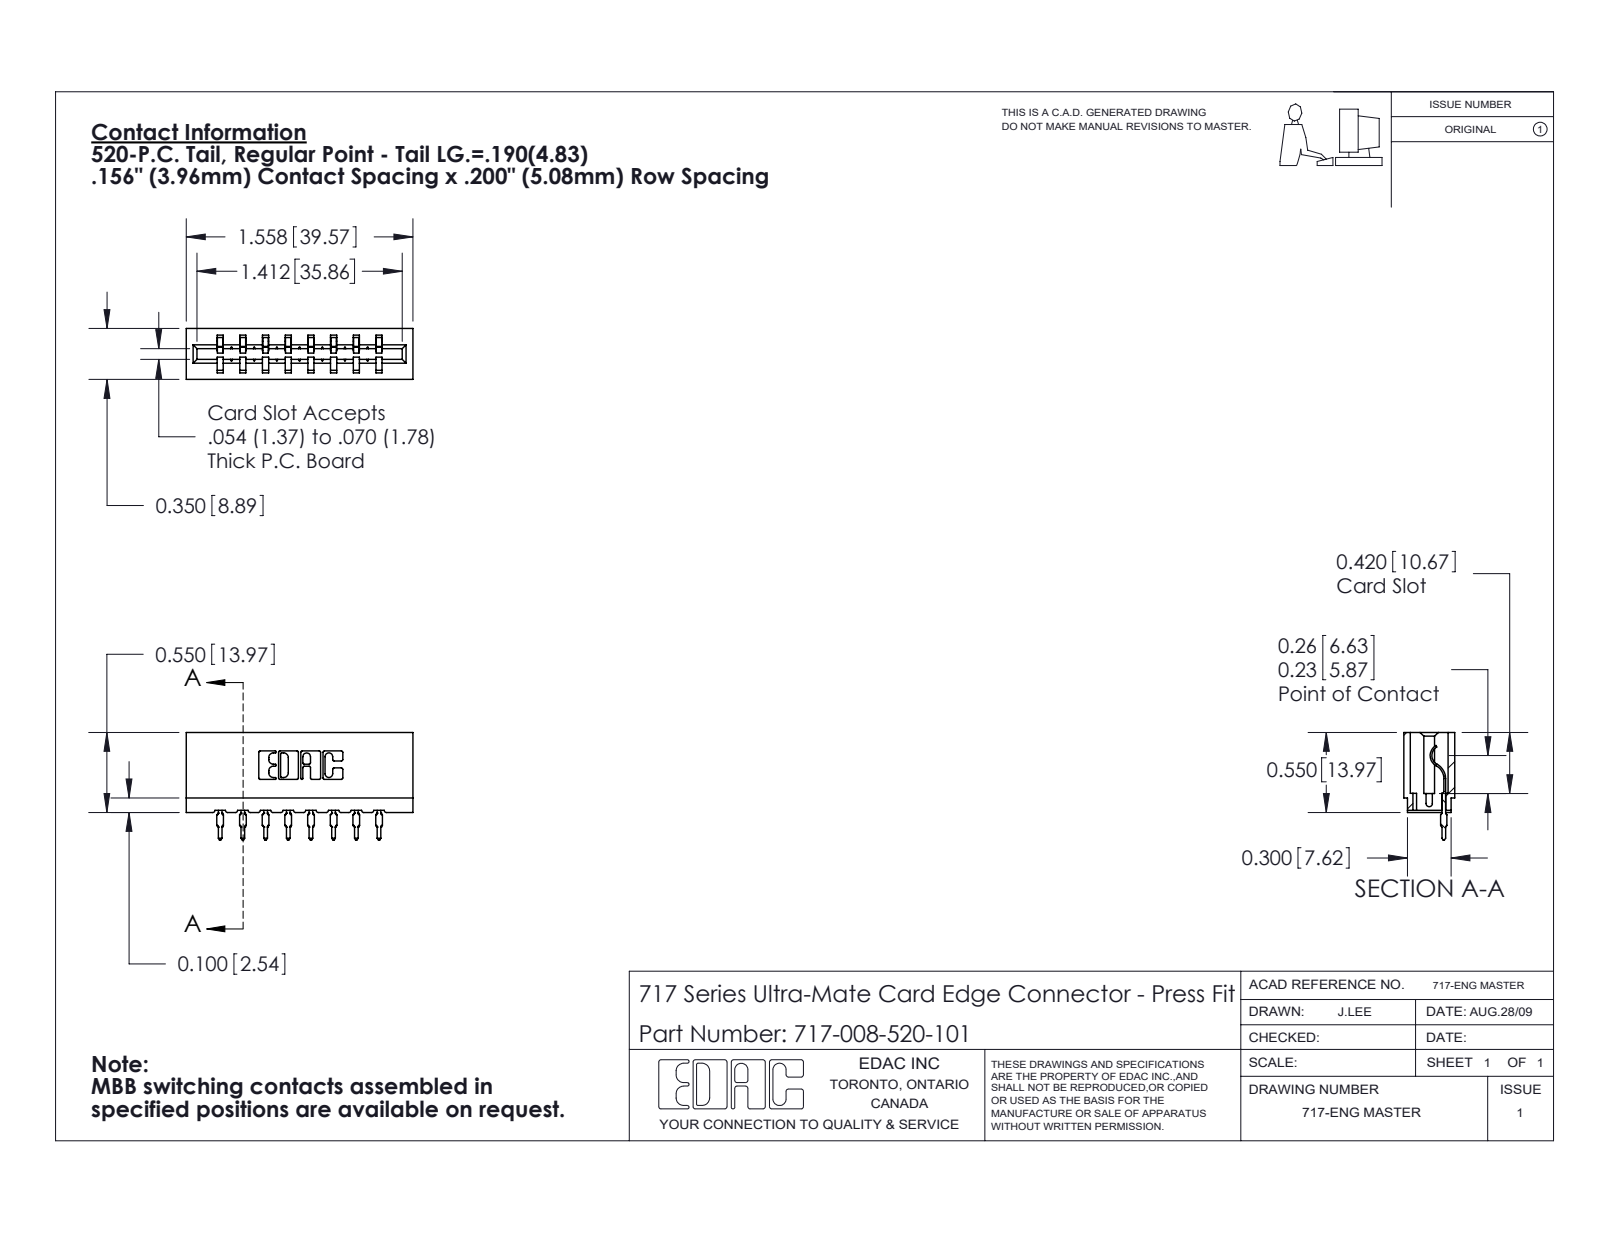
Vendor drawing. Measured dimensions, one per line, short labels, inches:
name: 717 Part_Insulator Option - 06; 717-008-520-101; 745-292-001_520
written by: SolidWorks 2020 (CONFIG_CONTROL_DESIGN)
unit: in
bodies: 9 solids, 998 faces (598 planar, 192 cylindrical, 208 other)
size: 1.558 × 0.739 × 0.35
volume: 0.213 in³; area: 6.926 in²
rounds: 22× R0.01, 16× R0.015, 16× R0.021, 6× R0.007, 6× R0.031, 4× R0.005, 4× R0.011, 3× R0.026
face distances: 0.212, 0.156, 0.138, 0.624, 0.468, 0.198, 0.312, 0.35, 0.042, 0.27
